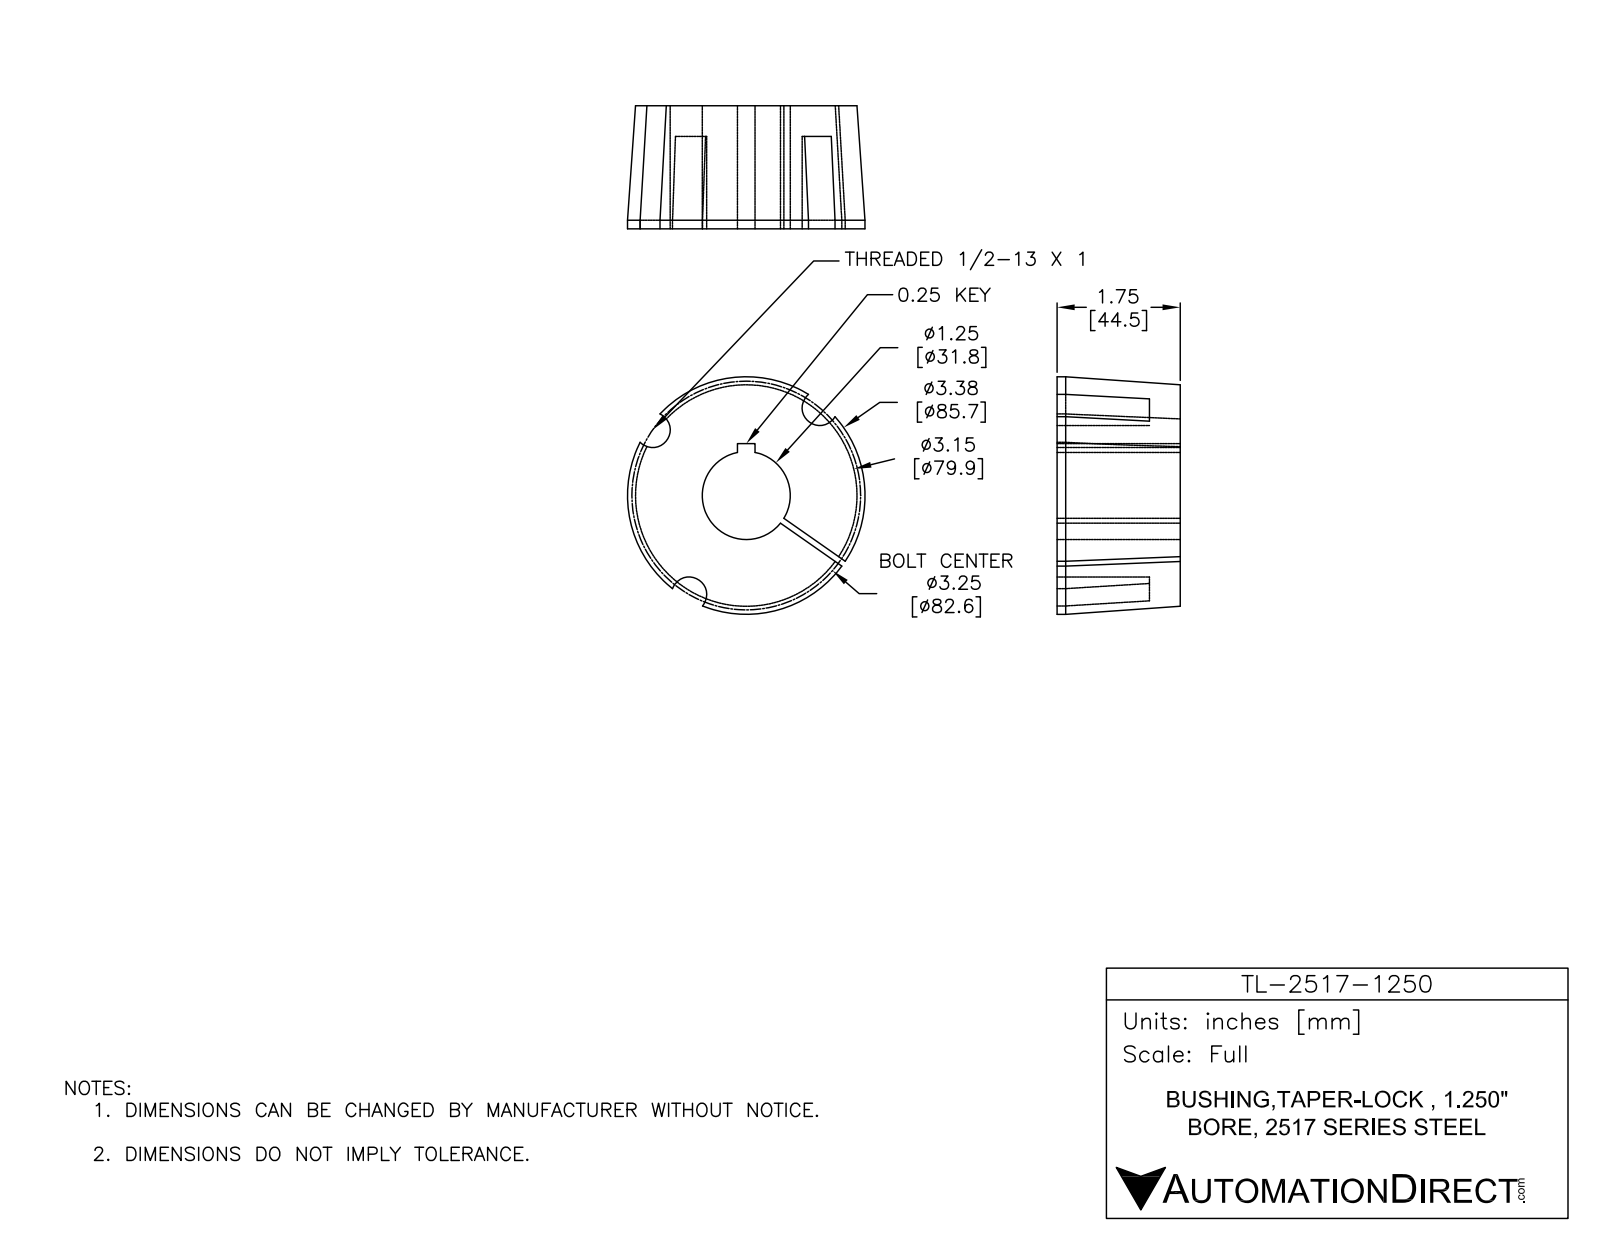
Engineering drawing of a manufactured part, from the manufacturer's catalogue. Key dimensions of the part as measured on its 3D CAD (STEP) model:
Part name (STEP PRODUCT): TL-2517-1250
STEP written by: SolidWorks 2014 (AUTOMOTIVE_DESIGN)
Units: inches
Bodies: 1 solid, 25 faces (9 planar, 13 cylindrical, 3 other)
Overall size (bounding box): 3.375 × 3.375 × 1.75
Volume: 11.89 in³ · Surface area: 43.57 in²
Round holes (diameter × count): ⌀1.25 ×1
Round bosses / shafts (diameter × count): ⌀3.375 ×1
Partial cylindrical surfaces — rounded edges, fillets, slot ends (radius × count): R0.25 ×3
Main face-to-face distances: 1.75, 0.085, 0.25, 0.437, 1.313
